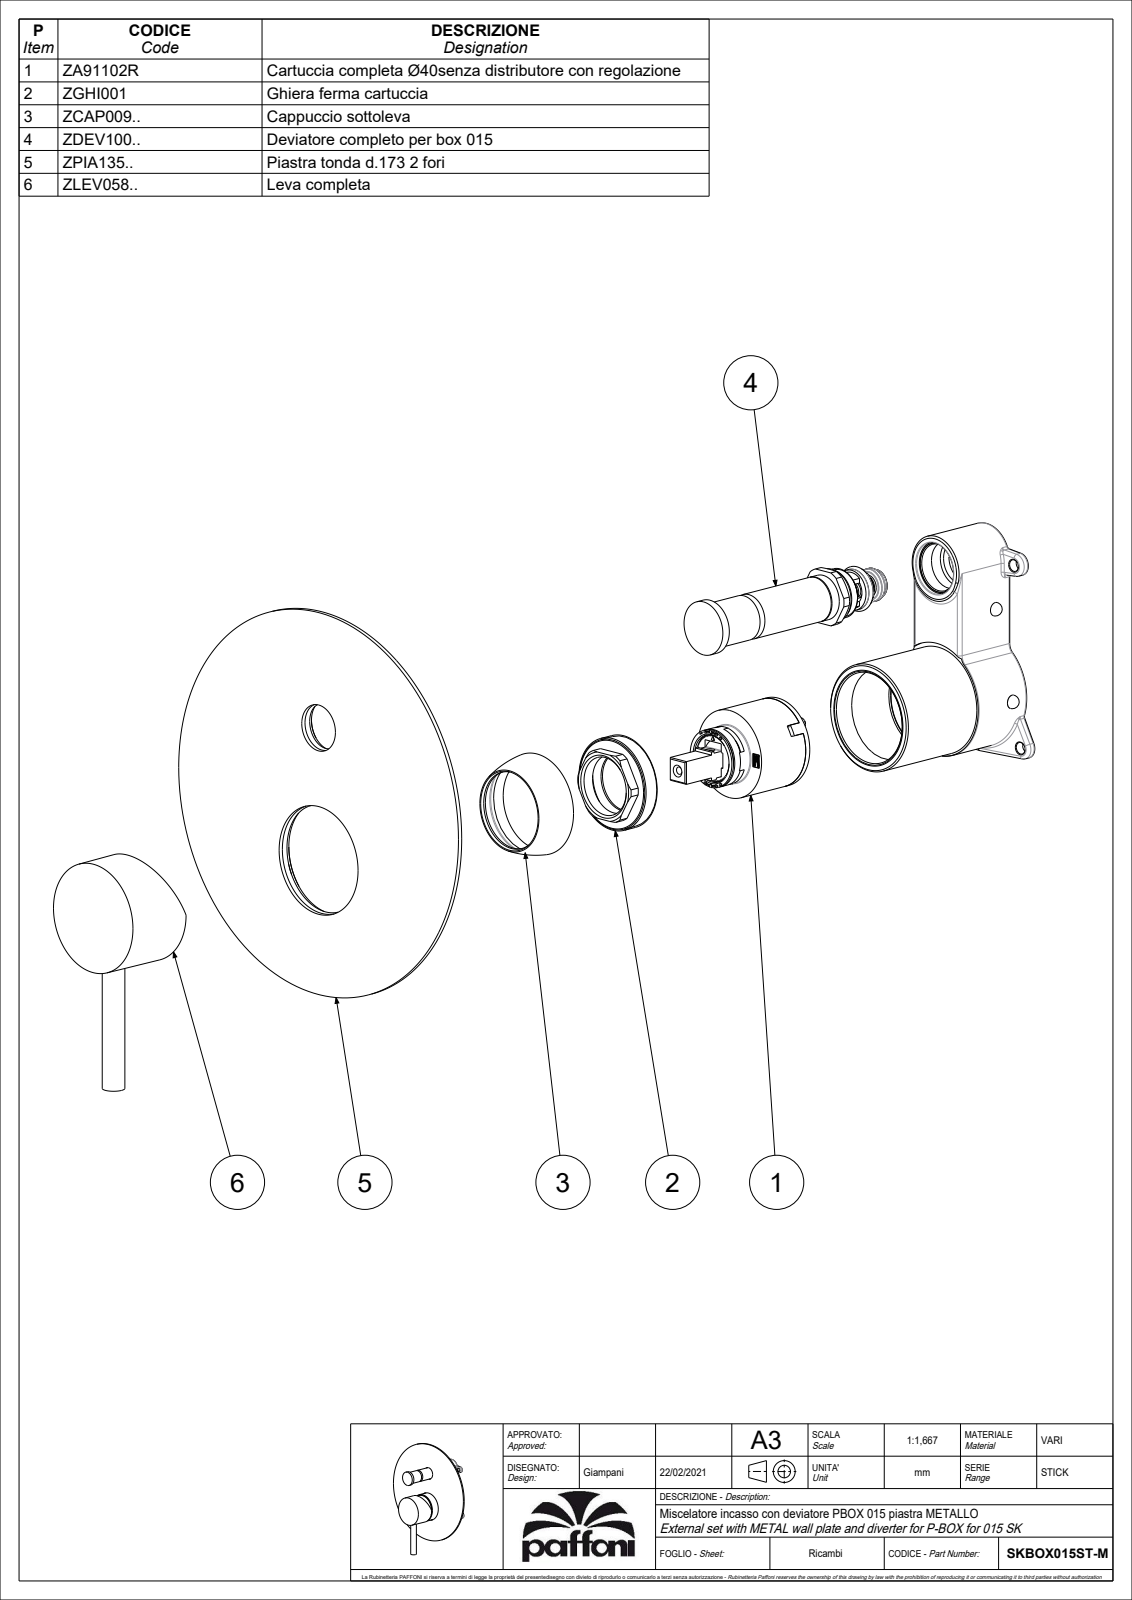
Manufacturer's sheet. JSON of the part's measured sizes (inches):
{"part_name": "SKBOX015ST-M", "step_written_by": "CREO PARAMETRIC BY PTC INC, 2020044 (CONFIG_CONTROL_DESIGN)", "units": "inches", "bodies": {"solids": 4, "faces": 818, "planar": 491, "cylindrical": 196, "other": 131}, "overall_size": [7.538, 6.811, 2.134], "volume_in3": 6.539, "surface_area_in2": 143.6, "round_holes": [[0.13, 3], [0.118, 1], [0.157, 1], [0.197, 1], [0.28, 1], [0.394, 1], [0.63, 1], [0.717, 1], [0.819, 1], [0.827, 1], [0.835, 1], [1.028, 1]], "round_bosses_or_shafts": [[6.811, 1], [1.894, 1], [1.555, 1], [1.299, 1], [1.016, 1], [1.014, 1], [0.951, 1], [0.945, 1]], "partial_cylinders_radius": [[0.008, 24], [0.256, 2], [0.02, 1], [0.276, 1], [0.396, 1], [0.469, 1], [0.484, 1]], "face_to_face_distances": [0.079, 1.843, 0.394, 1.921, 0.02, 0.295, 0.315, 0.122, 1.528, 0.272], "hole_center_spacings": [0.064, 0.543, 2.362, 2.426]}
